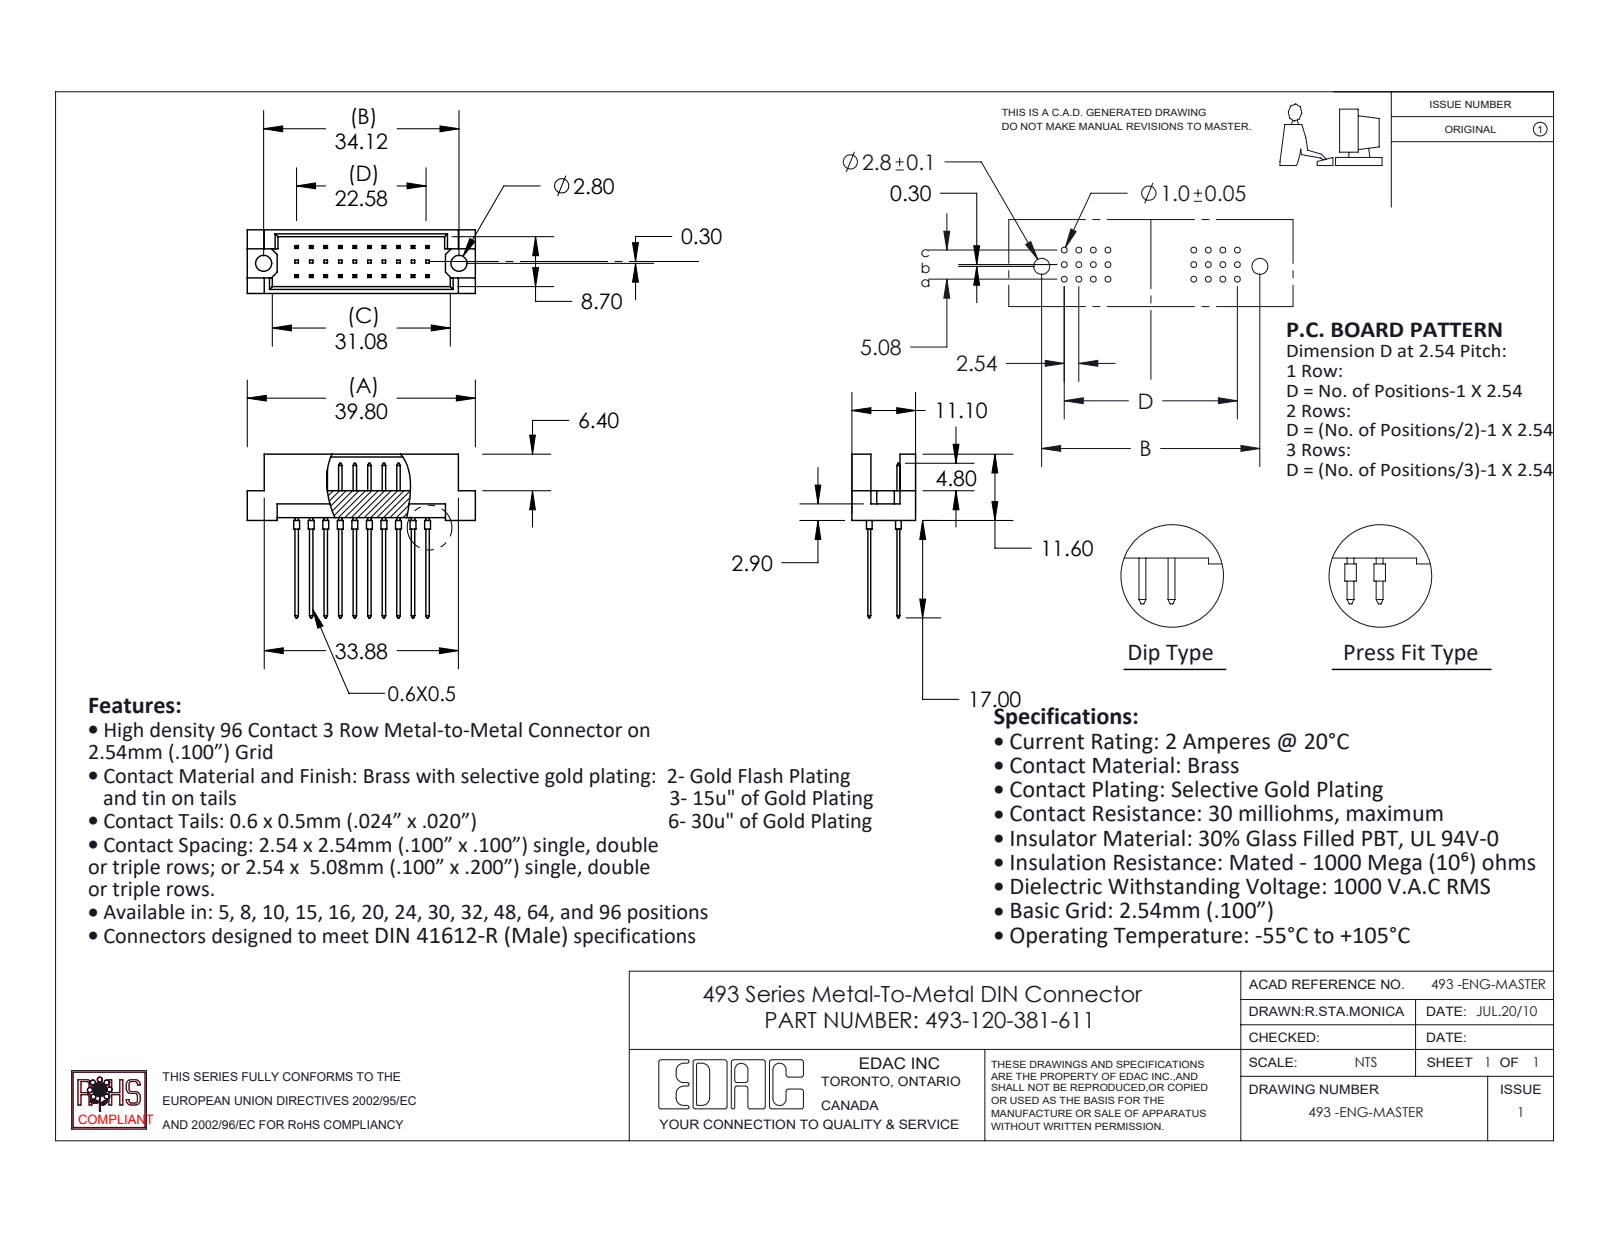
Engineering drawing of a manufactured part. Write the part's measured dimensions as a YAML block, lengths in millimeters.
part_name: "493-290_81; 493 Part_30; 493-124-381-321"
step_written_by: "SolidWorks 2020 (CONFIG_CONTROL_DESIGN)"
units: millimeters
bodies: {solids: 21, faces: 612, planar: 568, cylindrical: 44, other: 0}
overall_size: [39.8, 28.6, 11.1]
volume: 2547
surface_area: 3966
round_holes:
  - {diameter: 2.8, count: 2}
round_bosses_or_shafts:
  - {diameter: 1, count: 20}
face_to_face_distances: [5.08, 2.54, 1.2, 9.9, 0.5, 11.1, 2.76, 3.26, 7.84, 8.34]
hole_center_spacings: [34.12]
